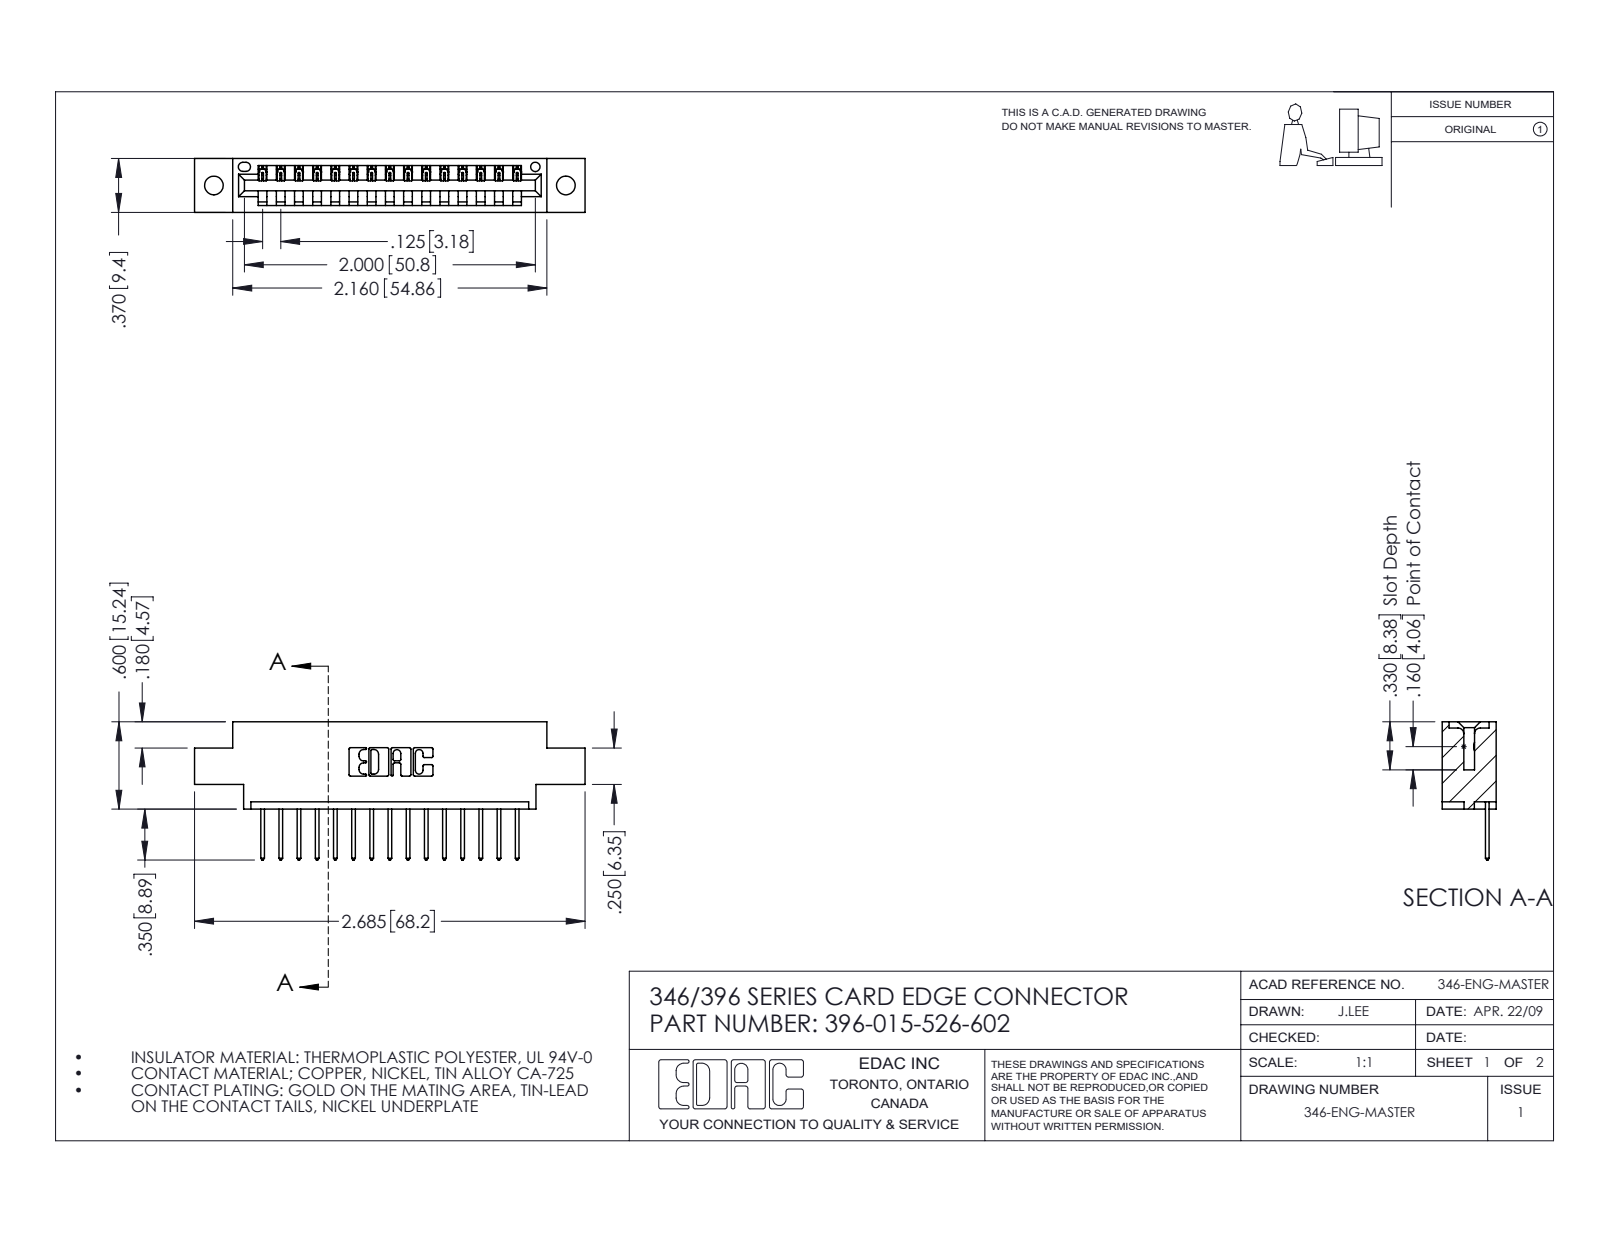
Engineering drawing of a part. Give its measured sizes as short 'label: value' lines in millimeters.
name: 345-292-001_345-293-126; 346 Part_0.170 Offset - 0.128 Dia; 396-015-526-602
written by: SolidWorks 2016 (CONFIG_CONTROL_DESIGN)
unit: mm
bodies: 16 solids, 996 faces (680 planar, 316 cylindrical, 0 other)
size: 68.2 × 24.1 × 9.4
volume: 6 150 mm³; area: 7 258 mm²
holes: 2× ⌀3.3, 1× ⌀1.6
rounds: 30× R0.2, 30× R0.3, 22× R0.3, 6× R0.2, 6× R0.8, 3× R0.7, 2× R0.8, 2× R1
face distances: 1.2, 8.2, 9.4, 6.4, 1.8, 7.6, 0.6, 3.8, 5.6, 2.5
hole spacings: 6.2, 56.2, 61.5
